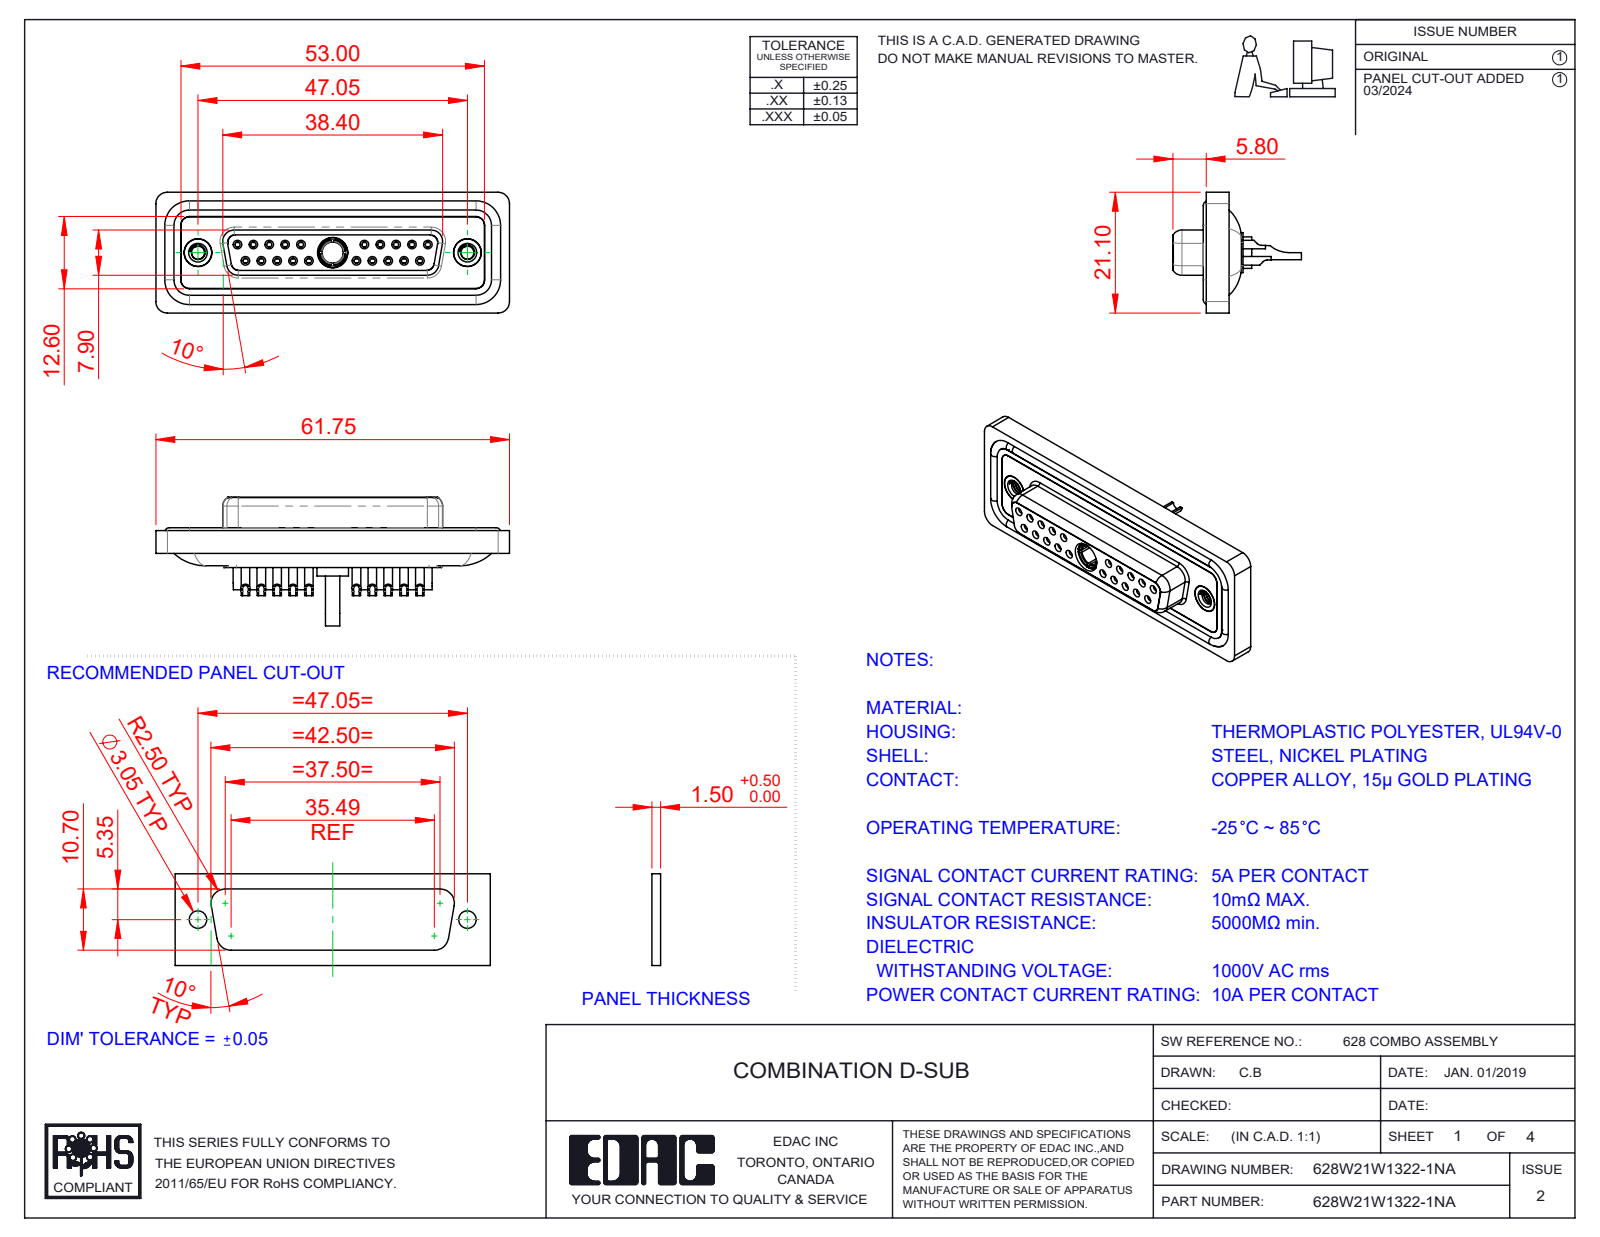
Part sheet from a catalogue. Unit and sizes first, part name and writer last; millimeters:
Units: millimetres
Overall size (bounding box): 61.75 × 22.45 × 21.1
Round holes (diameter × count): ⌀0.9 ×20, ⌀1 ×20, ⌀1.1 ×20, ⌀1.5 ×20, ⌀2 ×20, ⌀1.6 ×10, ⌀1.7 ×10, ⌀4.85 ×3, ⌀2.26 ×2, ⌀4 ×2, ⌀4.05 ×2, ⌀5 ×2
Round bosses / shafts (diameter × count): ⌀2.2 ×20, ⌀1.6 ×14, ⌀4.95 ×2, ⌀4.8 ×2, ⌀5.5 ×1, ⌀5.2 ×1, ⌀4.96 ×1, ⌀4.75 ×1
Partial cylindrical surfaces — rounded edges, fillets, slot ends (radius × count): R1.5 ×22, R2 ×18, R1.35 ×8, R1.6 ×8, R1 ×6, R0.25 ×4, R0.5 ×4, R0.6 ×4
Main face-to-face distances: 0.4, 1.8, 7.45, 5.65, 6.6, 0.5, 1.6, 7.05, 2.9, 1.1
Hole centre spacings: 3.16, 2.77, 5.54, 5.03, 8.31, 7.48, 16.62, 19.39
Volume: 8 414 mm³ · Surface area: 14 257 mm²
Bodies: 29 solids, 1563 faces (476 planar, 636 cylindrical, 451 other)
Part name (STEP PRODUCT): 628Combo Shell Rear_25 Contacts; 628Combo Contact Row 2_22; 628Combo Waterproof Housing_25 Contacts; 628Combo Housing_21W1 (+5 more)
STEP written by: SolidWorks 2023 (CONFIG_CONTROL_DESIGN)
